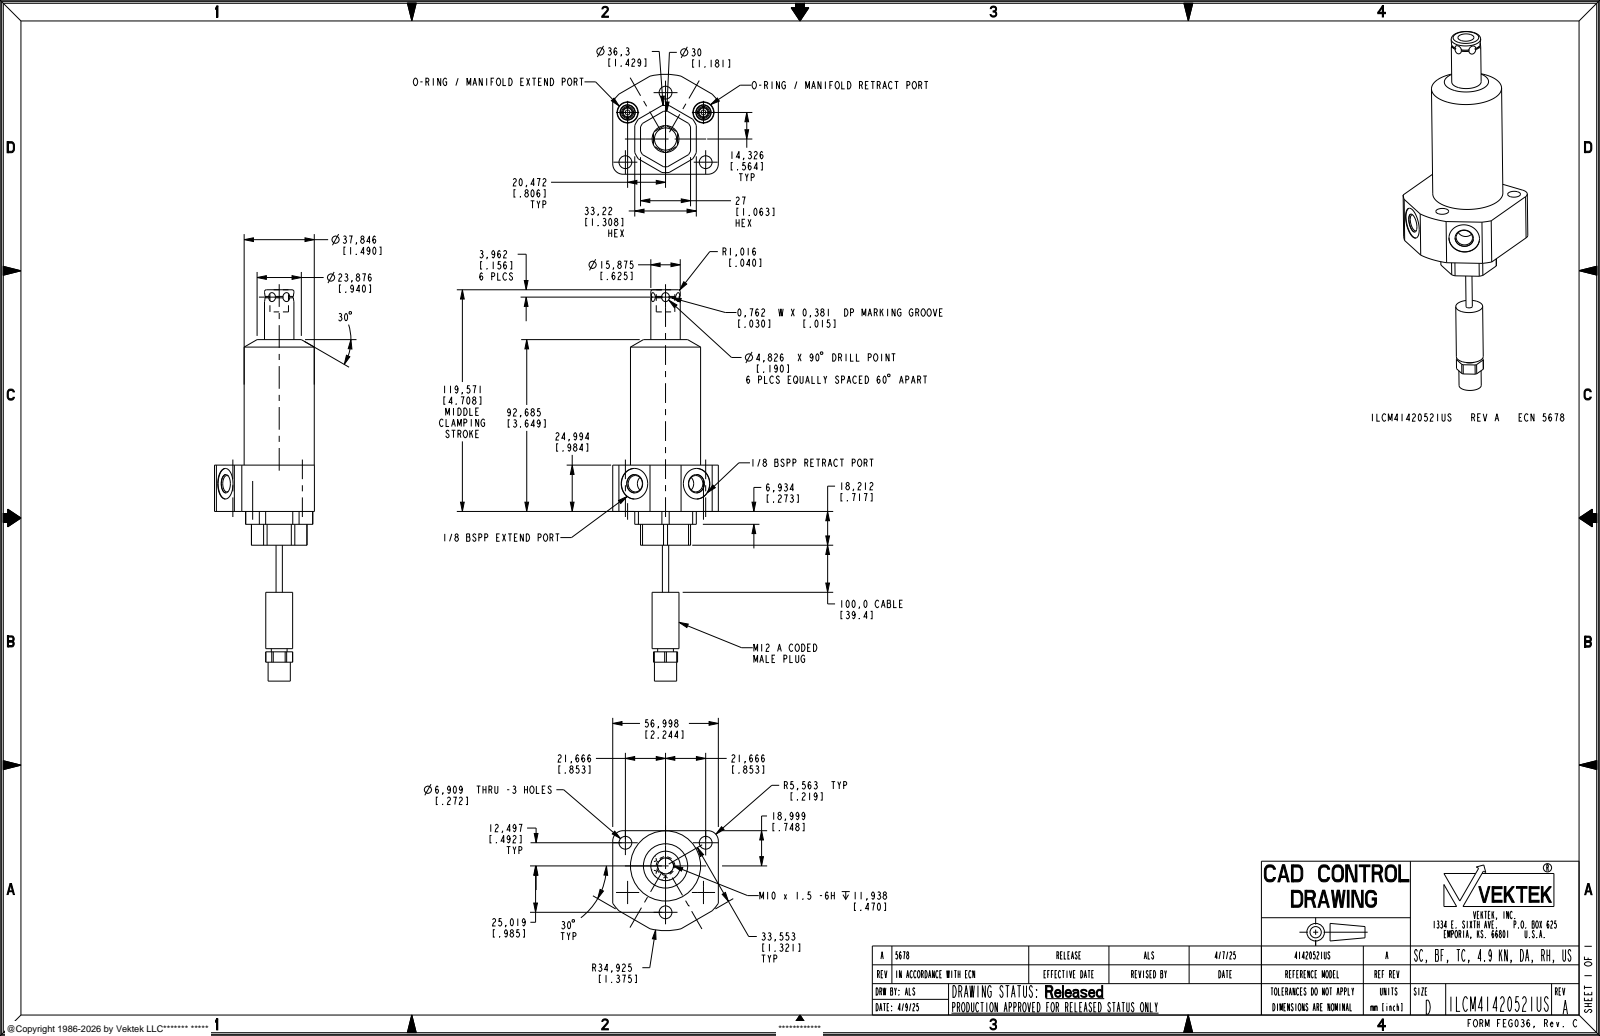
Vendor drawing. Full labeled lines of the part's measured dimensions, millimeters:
Part name (STEP PRODUCT): ILCM41420521US
STEP written by: CREO PARAMETRIC BY PTC INC, 2021164 (AUTOMOTIVE_DESIGN)
Units: millimetres
Bodies: 1 solid, 194 faces (79 planar, 81 cylindrical, 34 other)
Overall size (bounding box): 211.09 × 69.92 × 65
Volume: 164 663 mm³ · Surface area: 27 760 mm²
Round holes (diameter × count): ⌀6.91 ×3, ⌀2.49 ×2, ⌀6.5 ×2, ⌀8.84 ×2, ⌀9.91 ×2, ⌀11.4 ×2, ⌀16.5 ×2, ⌀8.61 ×1
Round bosses / shafts (diameter × count): ⌀5.49 ×2, ⌀37.85 ×1, ⌀15.88 ×1, ⌀14.5 ×1, ⌀11.99 ×1, ⌀10.01 ×1, ⌀8.51 ×1, ⌀3.4 ×1
Partial cylindrical surfaces — rounded edges, fillets, slot ends (radius × count): R5.56 ×2, R7.56 ×1, R15 ×1, R18.15 ×1, R34.92 ×1
Main face-to-face distances: 24.99, 57, 18.22, 43.21, 3.11, 30.11, 27, 11.28, 6.94, 31.93
Hole centre spacings: 25.02, 23.09, 24.99, 26.86, 43.33, 49.96, 40.94, 43.34
